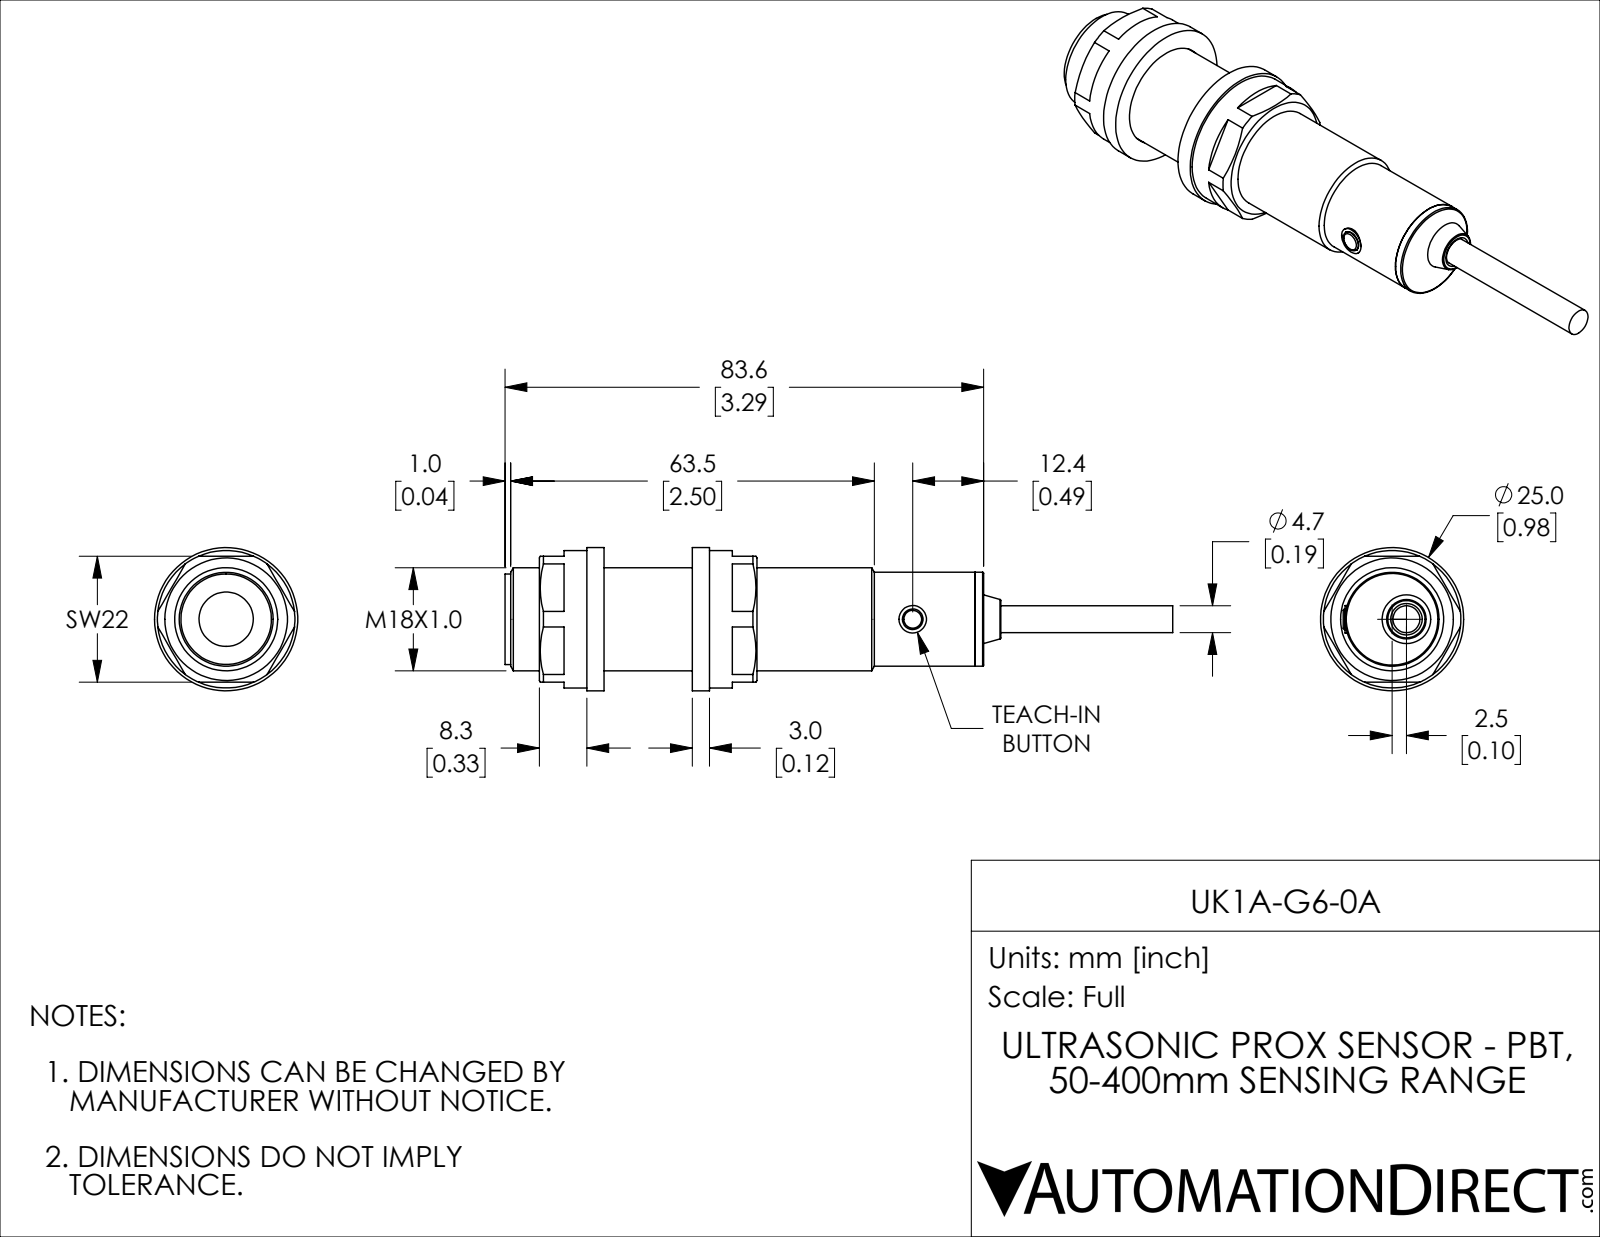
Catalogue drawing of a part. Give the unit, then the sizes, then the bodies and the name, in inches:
Units: inches
Overall size (bounding box): 4.591 × 0.984 × 0.984
Round holes (diameter × count): ⌀0.185 ×2, ⌀0.142 ×1, ⌀0.374 ×1, ⌀0.709 ×1, ⌀0.717 ×1
Round bosses / shafts (diameter × count): ⌀0.984 ×1, ⌀0.945 ×1, ⌀0.646 ×1, ⌀0.622 ×1, ⌀0.213 ×1, ⌀0.189 ×1
Main face-to-face distances: 0.118, 0.724, 0.843, 2.669, 1.827, 0.524, 1.366, 3.193, 0.642, 2.551
Hole centre spacings: 0.098
Volume: 1.539 in³ · Surface area: 17.7 in²
Bodies: 10 solids, 107 faces (49 planar, 40 cylindrical, 18 other)
Part name (STEP PRODUCT): UK1A-G6-0A
STEP written by: SolidWorks 2018 (AUTOMOTIVE_DESIGN)
